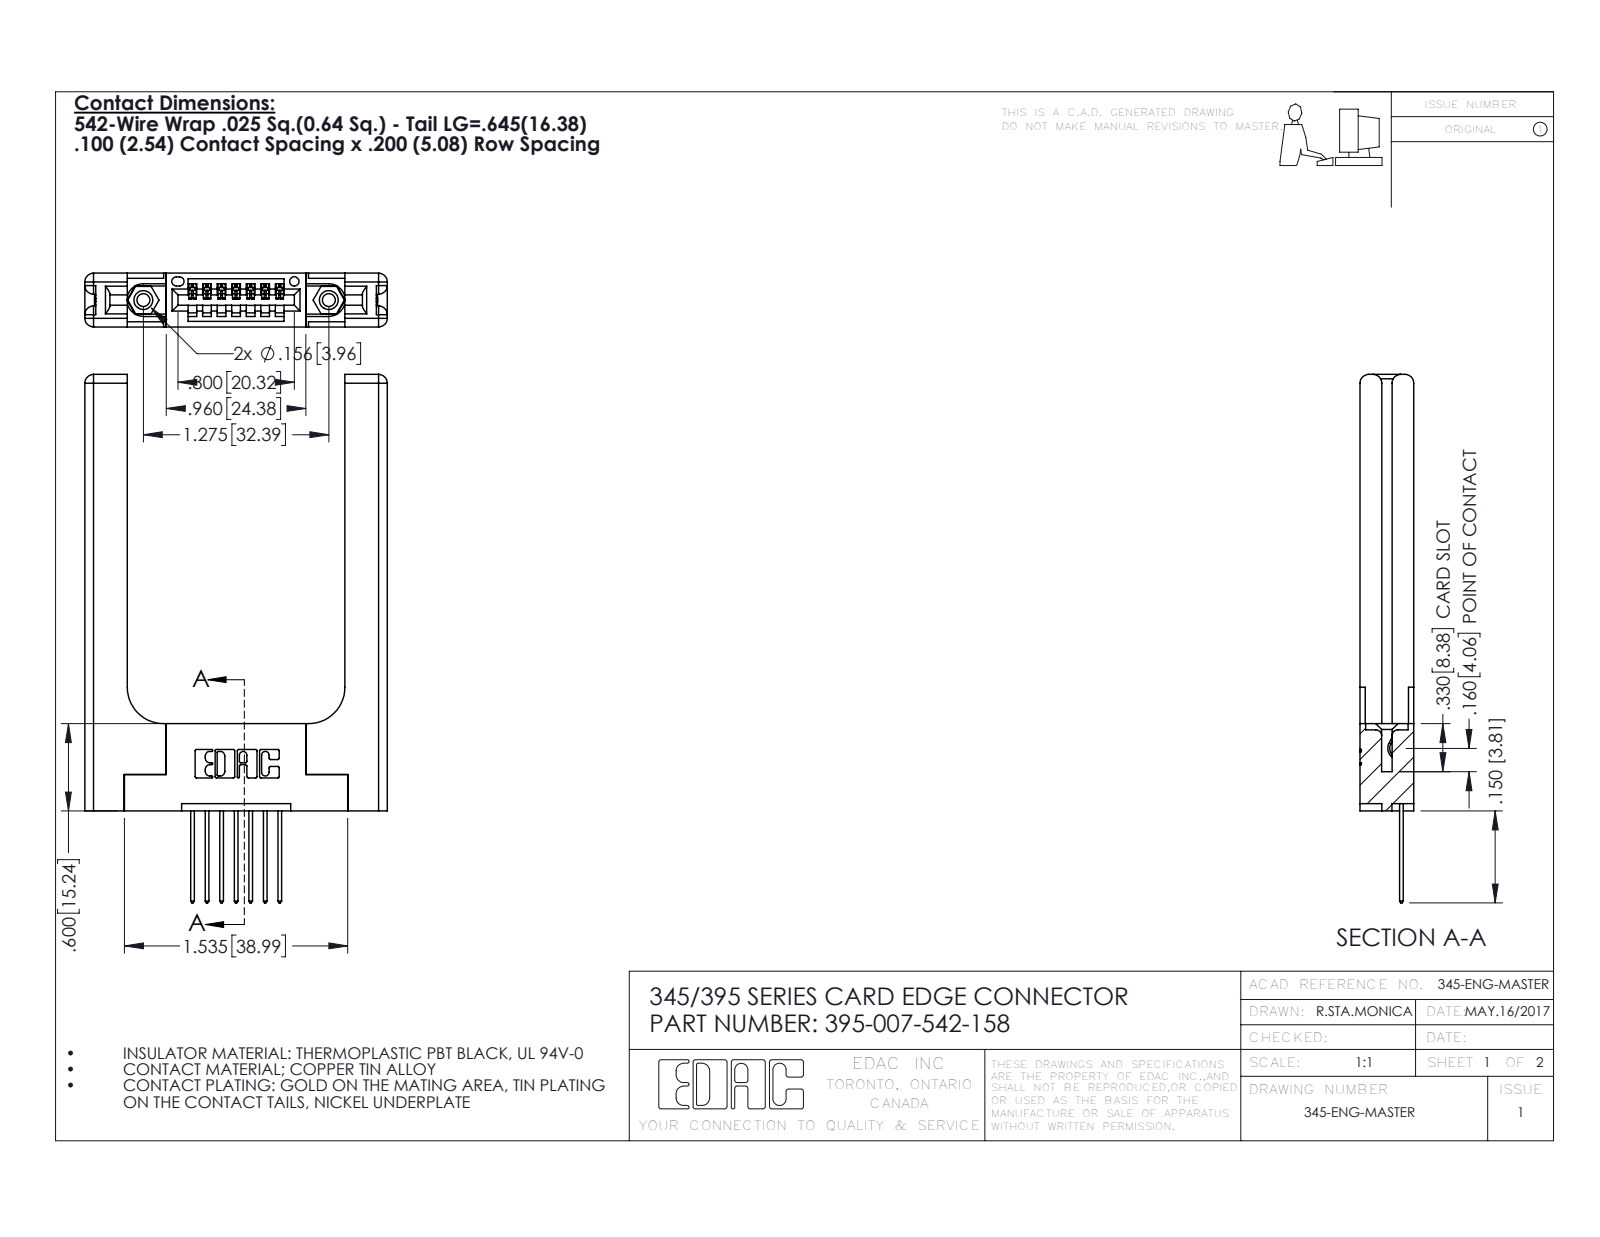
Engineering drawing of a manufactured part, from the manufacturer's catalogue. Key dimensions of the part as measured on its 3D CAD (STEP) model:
Part name (STEP PRODUCT): 395-007-542-158; 345 Part_Flush Mounting Lugs - 0.156 Dia-TH; 345-220-058_345-220-058; 345-292-001_345-293-142 (+1 more)
STEP written by: SolidWorks 2016 (CONFIG_CONTROL_DESIGN)
Units: inches
Bodies: 12 solids, 788 faces (508 planar, 220 cylindrical, 60 other)
Overall size (bounding box): 3.632 × 2.079 × 0.37
Volume: 0.809 in³ · Surface area: 17.41 in²
Round holes (diameter × count): ⌀0.089 ×2, ⌀0.125 ×2, ⌀0.156 ×2, ⌀0.064 ×1
Round bosses / shafts (diameter × count): ⌀0.155 ×2
Partial cylindrical surfaces — rounded edges, fillets, slot ends (radius × count): R0.01 ×22, R0.06 ×16, R0.006 ×14, R0.01 ×14, R0.007 ×6, R0.031 ×6, R0.026 ×3, R0.03 ×2
Main face-to-face distances: 0.37, 0.15, 0.22, 0.072, 0.077, 0.148, 0.298, 1.496, 0.2, 0.071
Hole centre spacings: 0.27, 1.045, 1.275
